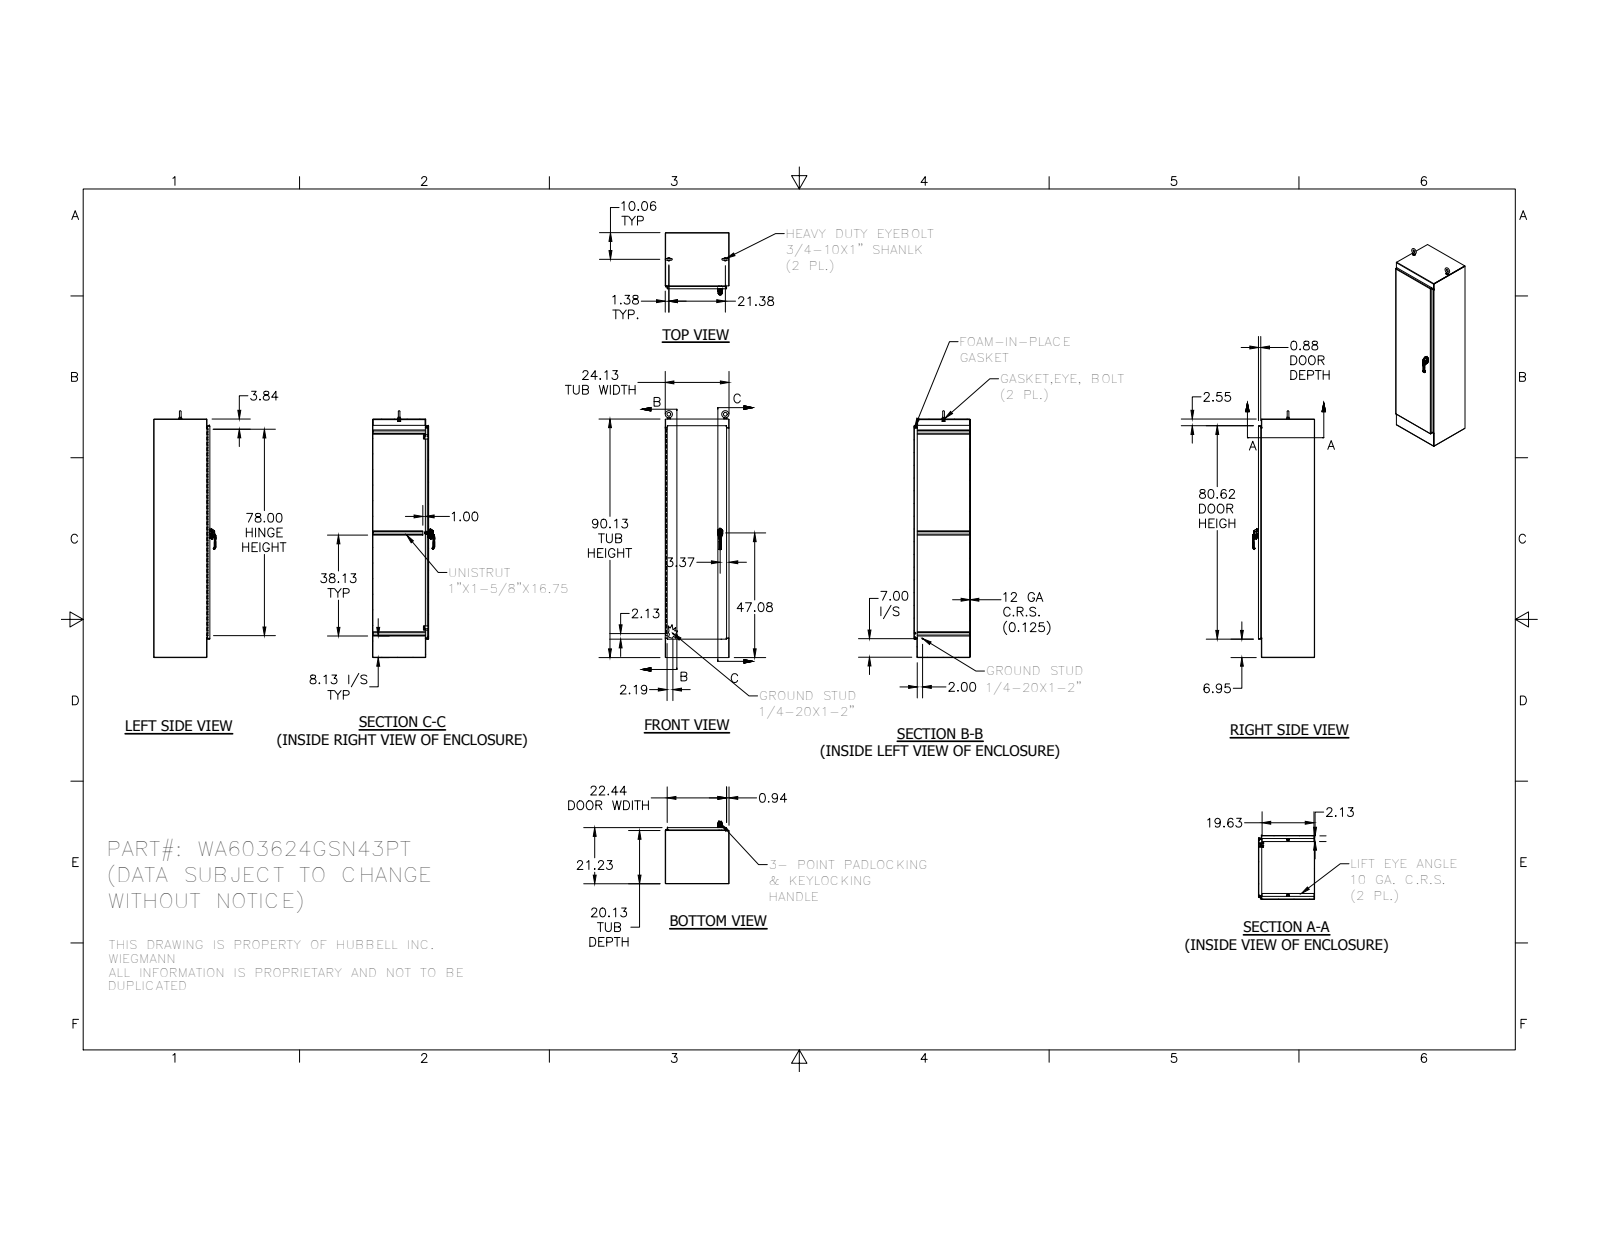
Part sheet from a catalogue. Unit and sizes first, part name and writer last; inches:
Units: inches
Overall size (bounding box): 93.248 × 24.125 × 21.23
Round holes (diameter × count): ⌀0.277 ×8, ⌀0.375 ×8, ⌀0.2 ×4, ⌀0.28 ×3, ⌀0.241 ×2, ⌀0.25 ×2, ⌀0.252 ×2, ⌀0.4 ×2, ⌀0.407 ×2, ⌀0.45 ×2, ⌀0.642 ×2, ⌀0.813 ×2
Round bosses / shafts (diameter × count): ⌀1.25 ×2, ⌀1.12 ×2, ⌀1 ×2, ⌀0.75 ×2, ⌀0.563 ×2, ⌀0.527 ×2, ⌀0.5 ×2, ⌀0.375 ×2
Partial cylindrical surfaces — rounded edges, fillets, slot ends (radius × count): R0.01 ×16, R0.125 ×16, R0.031 ×15, R0.156 ×15, R0.05 ×14, R0.019 ×12, R0.053 ×12, R0.086 ×12
Main face-to-face distances: 0.125, 24, 0.125, 20.98, 21.105, 23.875, 24.125, 21.23, 21.104, 90
Hole centre spacings: 8.667, 26, 17.333, 34.667, 71.883, 72.633, 0.762, 0.764
Volume: 1 311 in³ · Surface area: 21 259 in²
Bodies: 52 solids, 1844 faces (833 planar, 691 cylindrical, 320 other)
Part name (STEP PRODUCT): HFW31233; 3862; HFW3121; WA902420FSN43PT (+8 more)
STEP written by: SolidWorks 2014 (AUTOMOTIVE_DESIGN)
